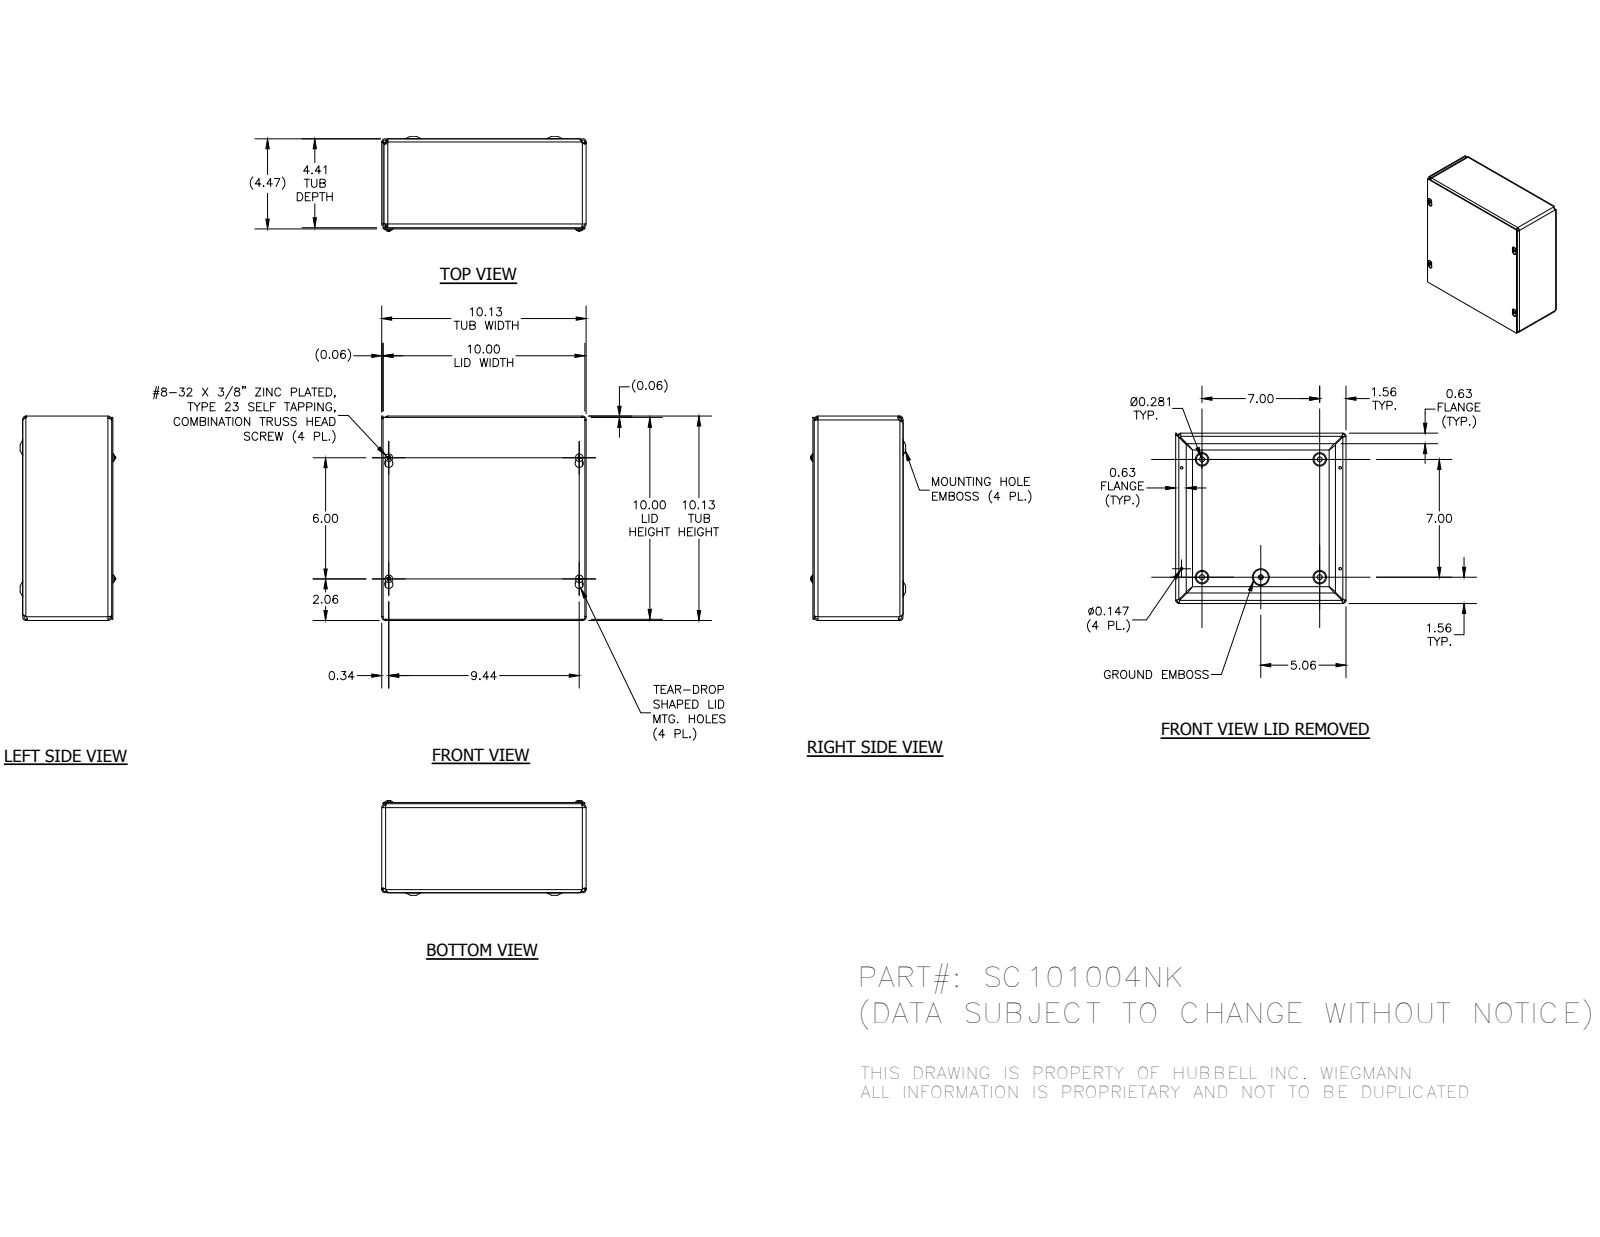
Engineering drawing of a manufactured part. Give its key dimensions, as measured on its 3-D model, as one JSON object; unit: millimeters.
{"part_name": "SC1010BKP; SC101004NKWRA; SC1010LID; 34056 (+1 more)", "step_written_by": "Autodesk Inventor 2014 (AUTOMOTIVE_DESIGN)", "units": "millimeters", "bodies": {"solids": 7, "faces": 357, "planar": 132, "cylindrical": 67, "other": 158}, "overall_size": [257.18, 257.18, 119.2], "volume_mm3": 428793, "surface_area_mm2": 551635, "round_holes": [[3.73, 4], [7.62, 4], [4.19, 1]], "round_bosses_or_shafts": [[9.75, 4], [4.17, 4], [5.8, 1]], "partial_cylinders_radius": [[3.17, 12], [4.75, 8], [1.4, 4], [1.57, 4], [2.38, 4], [2.97, 4], [3.15, 4], [3.96, 4]], "face_to_face_distances": [1.57, 110.32, 255.6, 111.89, 1.59, 111.91, 113.48, 254.03, 1.58, 257.17], "hole_center_spacings": [167.98, 177.8, 33.45, 33.46, 88.9, 152.4, 198.79, 209.14]}
